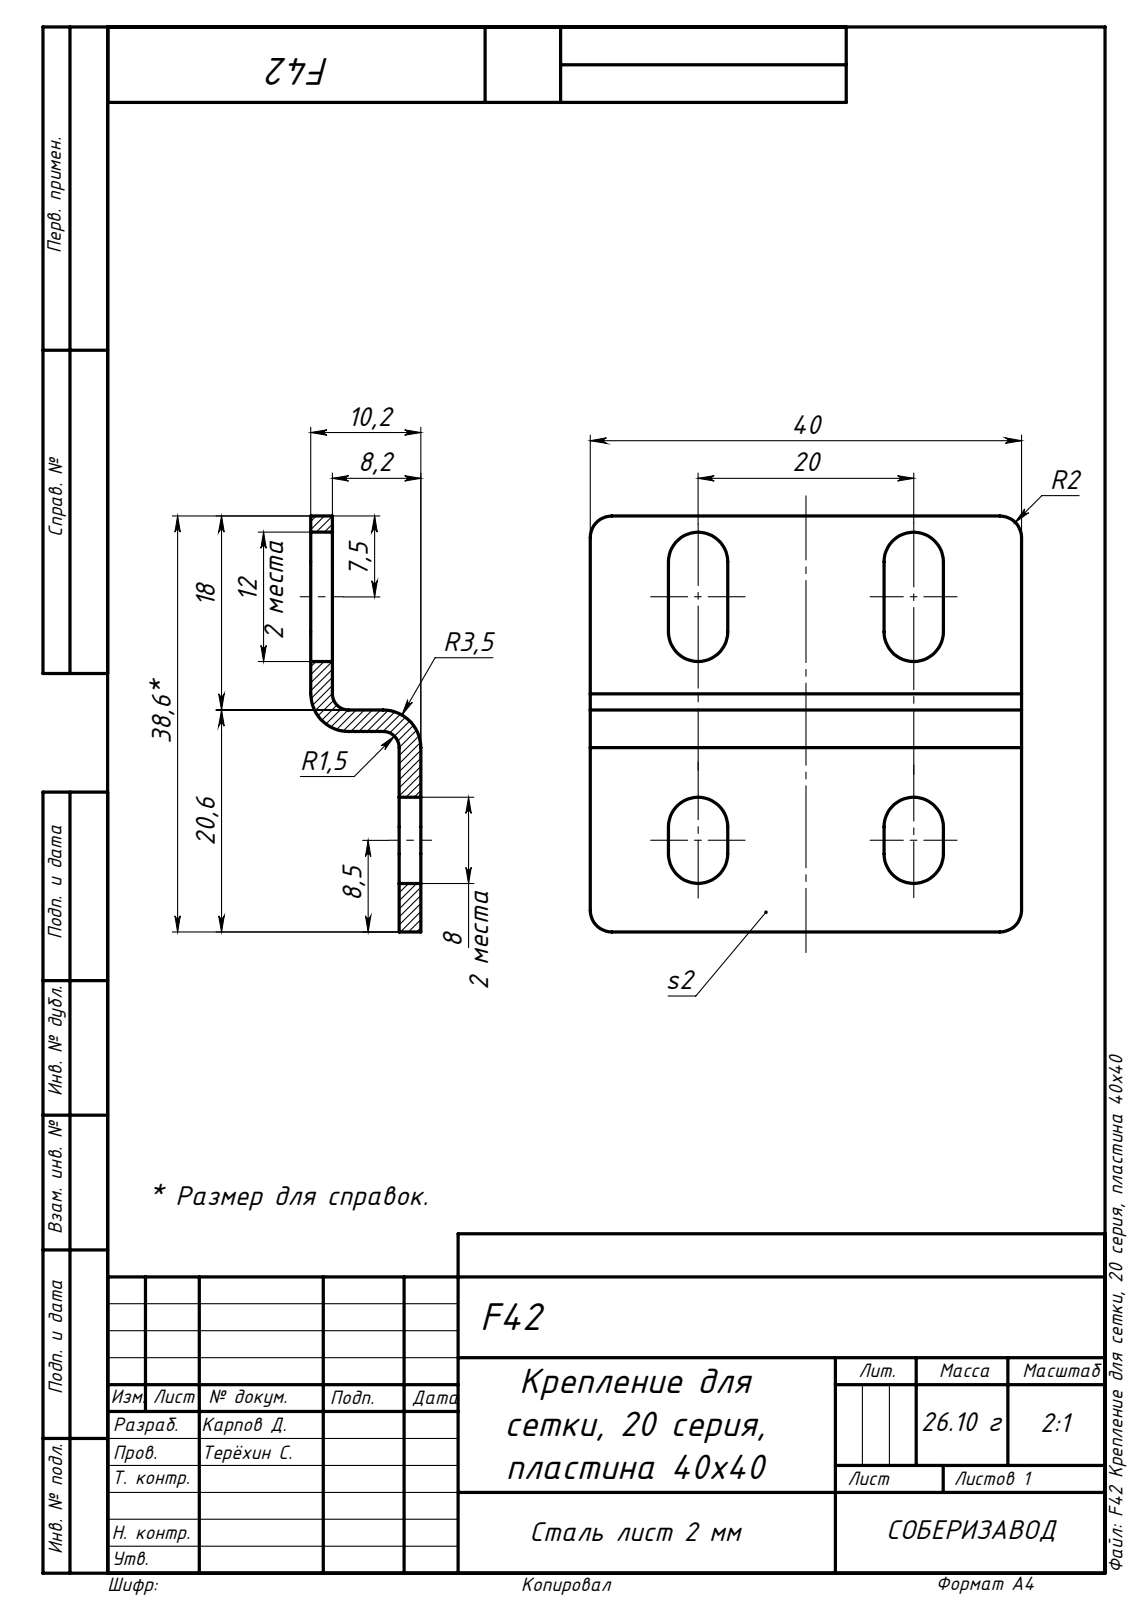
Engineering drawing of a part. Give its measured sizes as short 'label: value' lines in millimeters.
name: F42 Крепление для сетки, 20 серия, пластина 40х40
written by: SolidWorks 2019 (AUTOMOTIVE_DESIGN)
unit: mm
bodies: 1 solid, 46 faces (26 planar, 20 cylindrical, 0 other)
size: 40 × 38.6 × 10.2
volume: 3 177 mm³; area: 3 719 mm²
rounds: 8× R2.75, 4× R2, 2× R1.5, 2× R3.5
face distances: 2, 8.2, 10.2, 6.2, 20, 40, 18.6, 20.6, 38.6, 18
